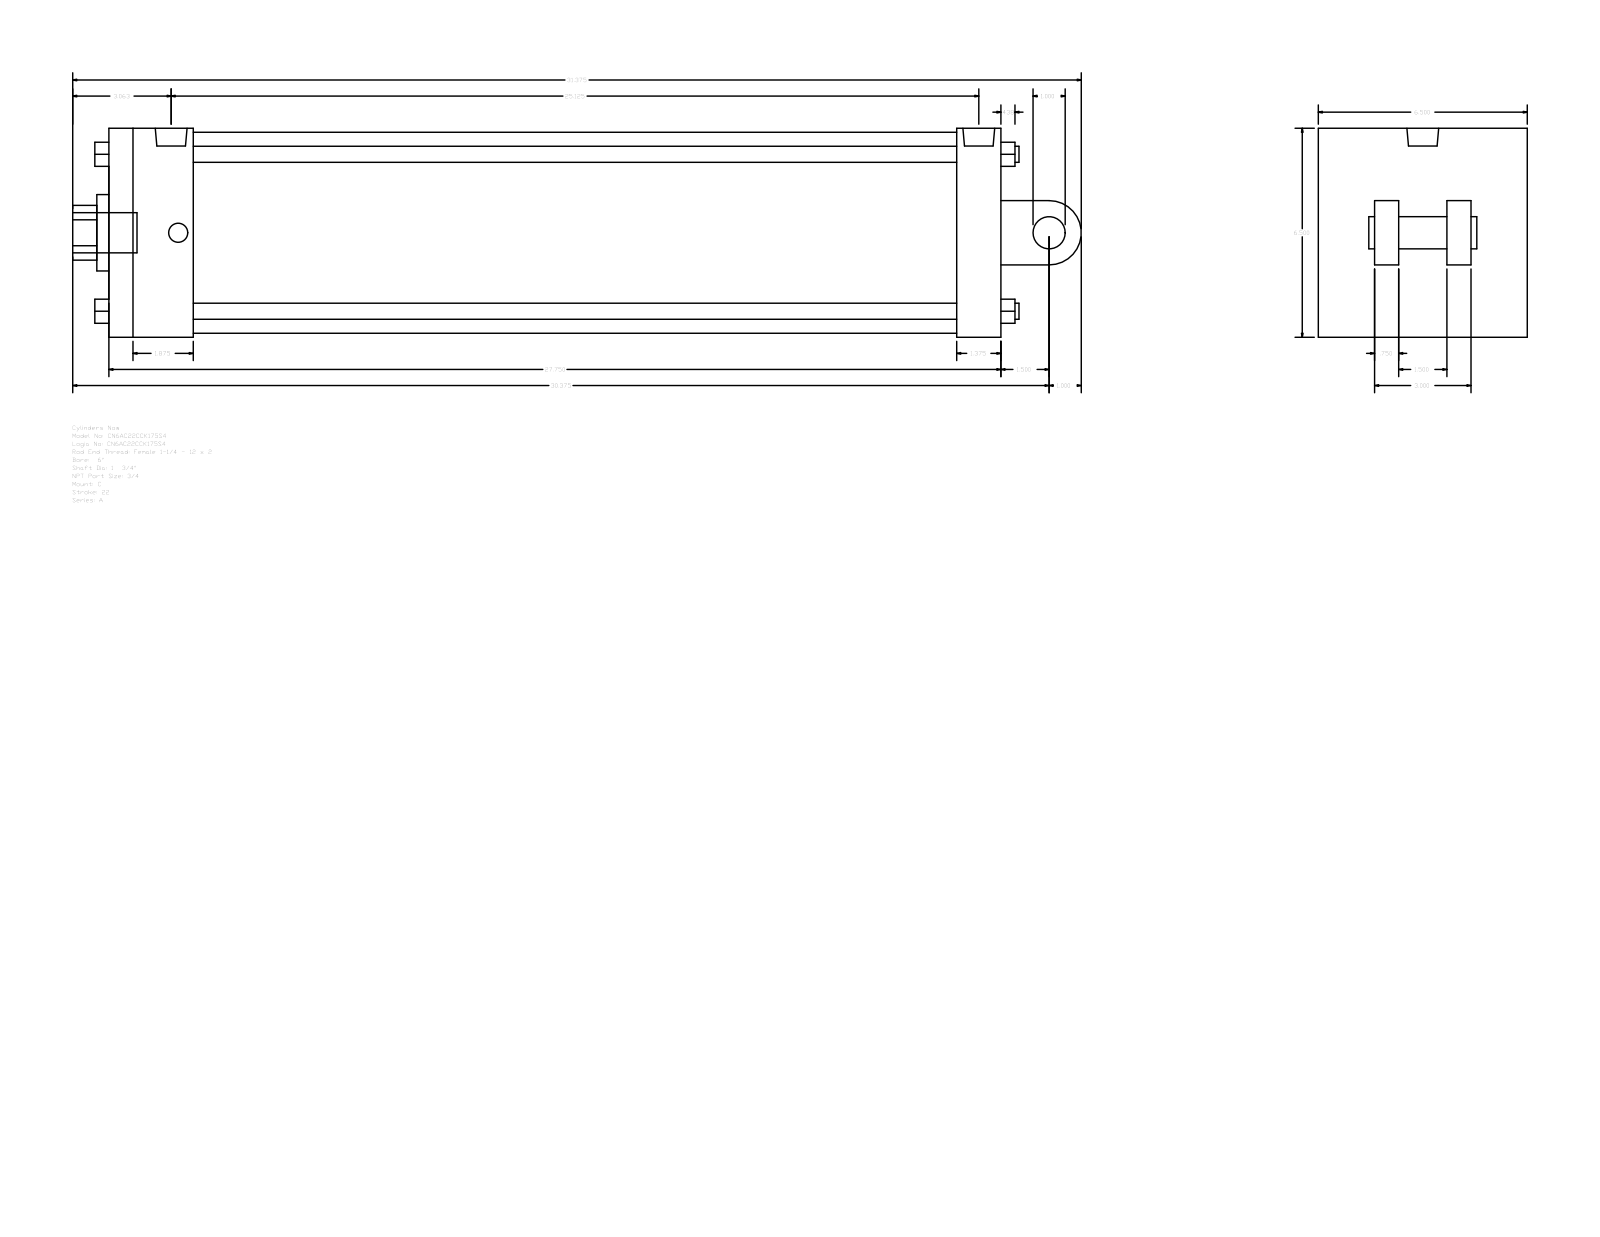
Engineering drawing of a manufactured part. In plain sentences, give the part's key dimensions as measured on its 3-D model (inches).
The part is named "A_C__0600_1.75". Its 3-D file was written by "GSSL Pune (CONFIG_CONTROL_DESIGN)". It is 0 solids with 135 faces: 102 planar, 33 cylindrical and 0 other. Overall it measures 31.375 by 6.5 by 6.5 inches. Round holes: 2 of diameter 0.594, 1 of diameter 0.989, 1 of diameter 1.75, 1 of diameter 2.375, 1 of diameter 6.25. Round bosses or shafts: 4 of diameter 0.5, 2 of diameter 0.594, 1 of diameter 1.25, 1 of diameter 1, 1 of diameter 0.989. Partial cylindrical surfaces (rounded edges, fillets, slot ends): 1 of radius 0.852, 1 of radius 1. The main face-to-face distances are 6.5, 27.75, 0.75, 2.25, 1.375, 2.625, 25.125, 26.375, 23.75, 1.75. The hole center spacings are 0.219.
